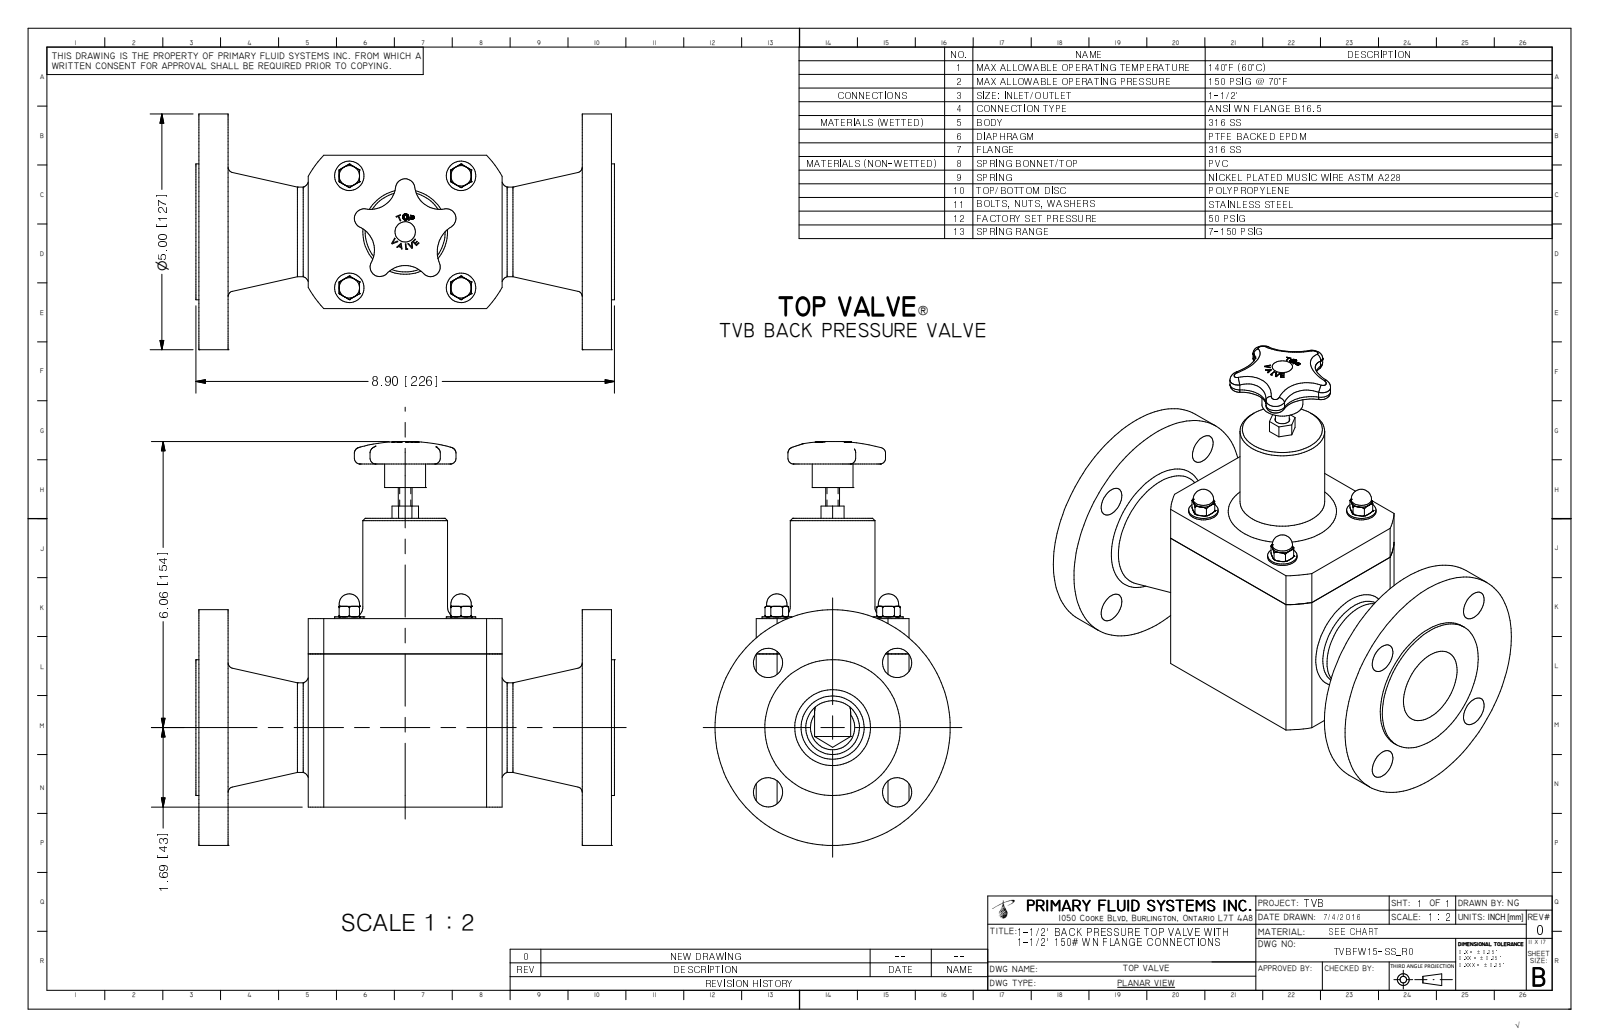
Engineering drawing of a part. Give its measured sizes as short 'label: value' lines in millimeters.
name: TVBFW15-SS-R0
written by: Autodesk Inventor 2009 (AUTOMOTIVE_DESIGN)
unit: mm
bodies: 1 solid, 361 faces (150 planar, 59 cylindrical, 152 other)
size: 225.9 × 217.6 × 127
volume: 1 371 000 mm³; area: 161 900 mm²
holes: 4× ⌀4.4, 4× ⌀15.7, 1× ⌀40.9
bosses: 4× ⌀15.9, 4× ⌀11, 4× ⌀9.5, 1× ⌀127, 1× ⌀73.2, 1× ⌀48.3, 1× ⌀45.7, 1× ⌀22.1
rounds: 5× R2.2, 5× R5.2, 4× R13.6, 4× R16.7, 1× R15.9, 1× R18.9, 1× R60.3
face distances: 15.7, 207, 82.6, 191.3, 222.8, 59, 163.8, 43.2, 148, 1.6
hole spacings: 49.3, 69.7, 60.3, 60.3, 85.3, 98.6
